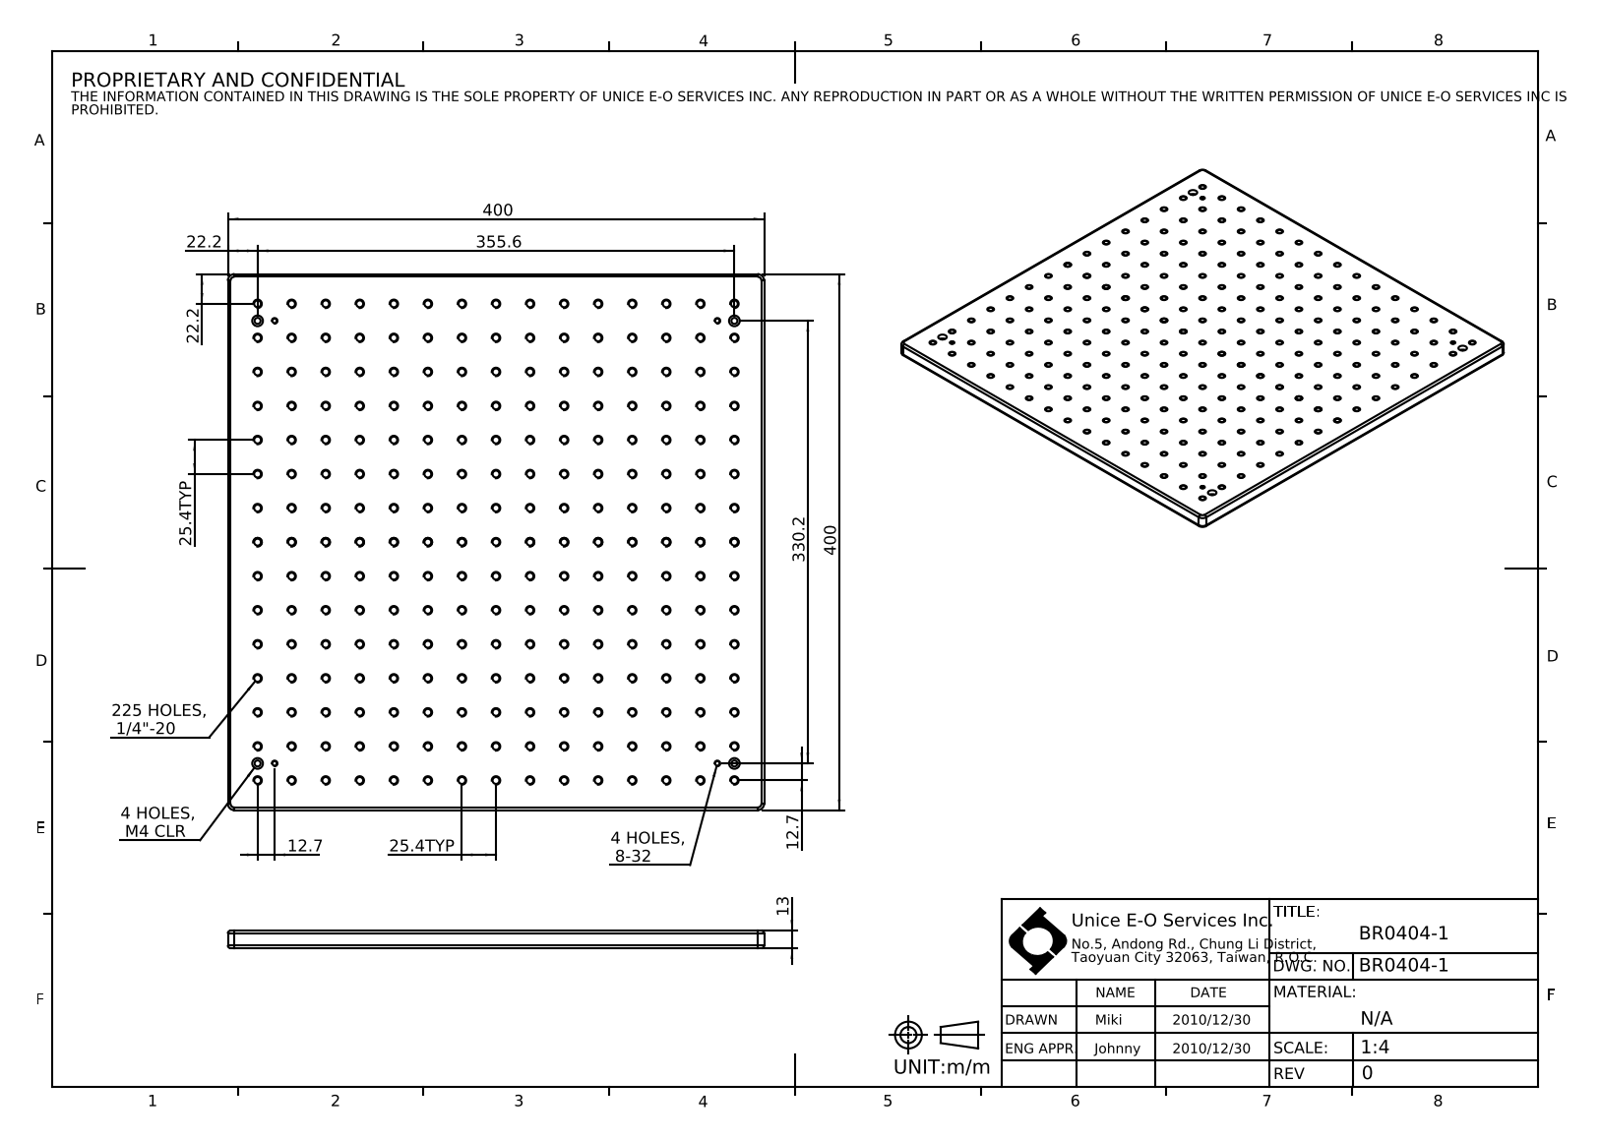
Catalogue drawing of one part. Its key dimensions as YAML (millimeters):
part_name: "BR0404-1"
step_written_by: "SolidWorks 2016 (CONFIG_CONTROL_DESIGN)"
units: millimeters
bodies: {solids: 1, faces: 504, planar: 10, cylindrical: 486, other: 8}
overall_size: [400, 400, 13]
volume: 2015000
surface_area: 376903
round_holes:
  - {diameter: 5.11, count: 225}
  - {diameter: 3.45, count: 4}
  - {diameter: 4.5, count: 4}
  - {diameter: 8, count: 4}
partial_cylinders:
  - {radius: 2, count: 8}
  - {radius: 5, count: 4}
face_to_face_distances: [13, 400, 8.6, 4.4]
hole_center_spacings: [25.4, 50.8, 76.2, 35.92, 56.8, 101.6, 80.32, 104.73]
